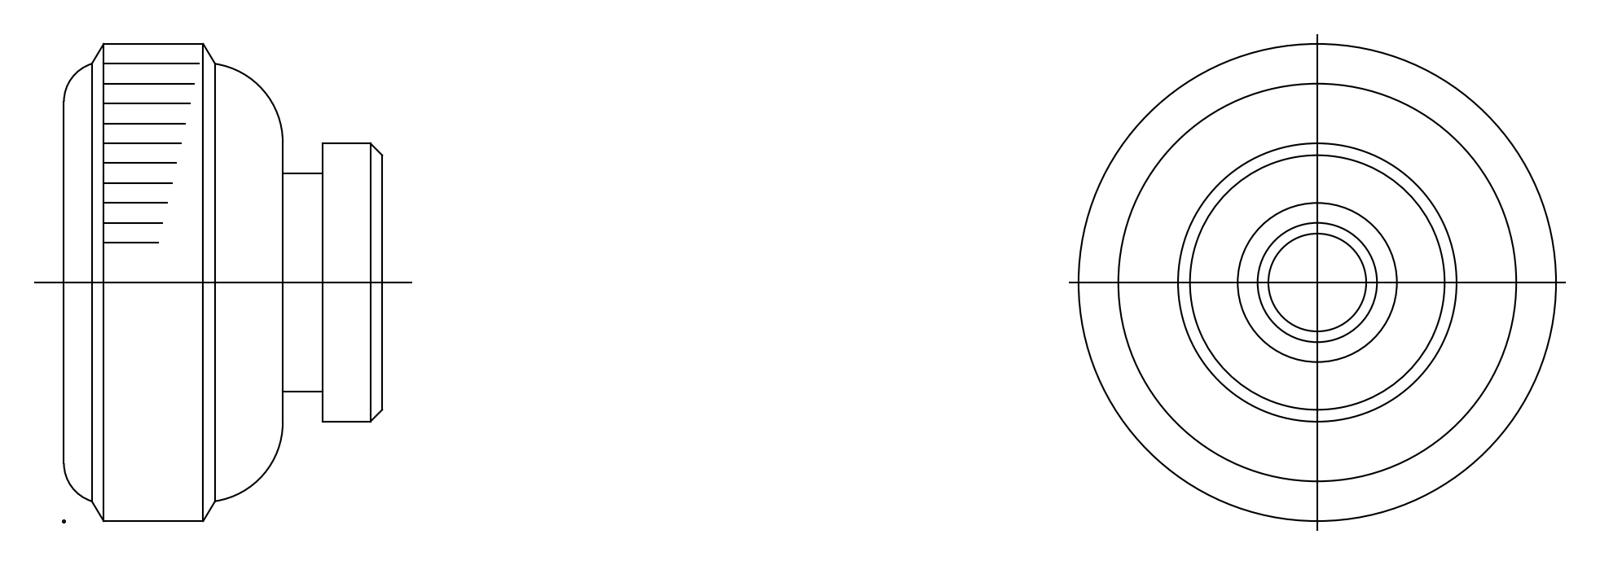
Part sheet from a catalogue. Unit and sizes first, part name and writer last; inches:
Units: inches
Overall size (bounding box): 0.472 × 0.472 × 0.315
Round holes (diameter × count): ⌀0.097 ×1, ⌀0.118 ×1
Round bosses / shafts (diameter × count): ⌀0.472 ×1, ⌀0.276 ×1, ⌀0.217 ×1
Main face-to-face distances: 0.315, 0.217, 0.098, 0.256, 0.039, 0.059
Volume: 0.036 in³ · Surface area: 0.756 in²
Bodies: 1 solid, 30 faces (4 planar, 10 cylindrical, 16 other)
STEP written by: spGate 20.6.3 (****-****-****-****) (AUTOMOTIVE_DESIGN)
